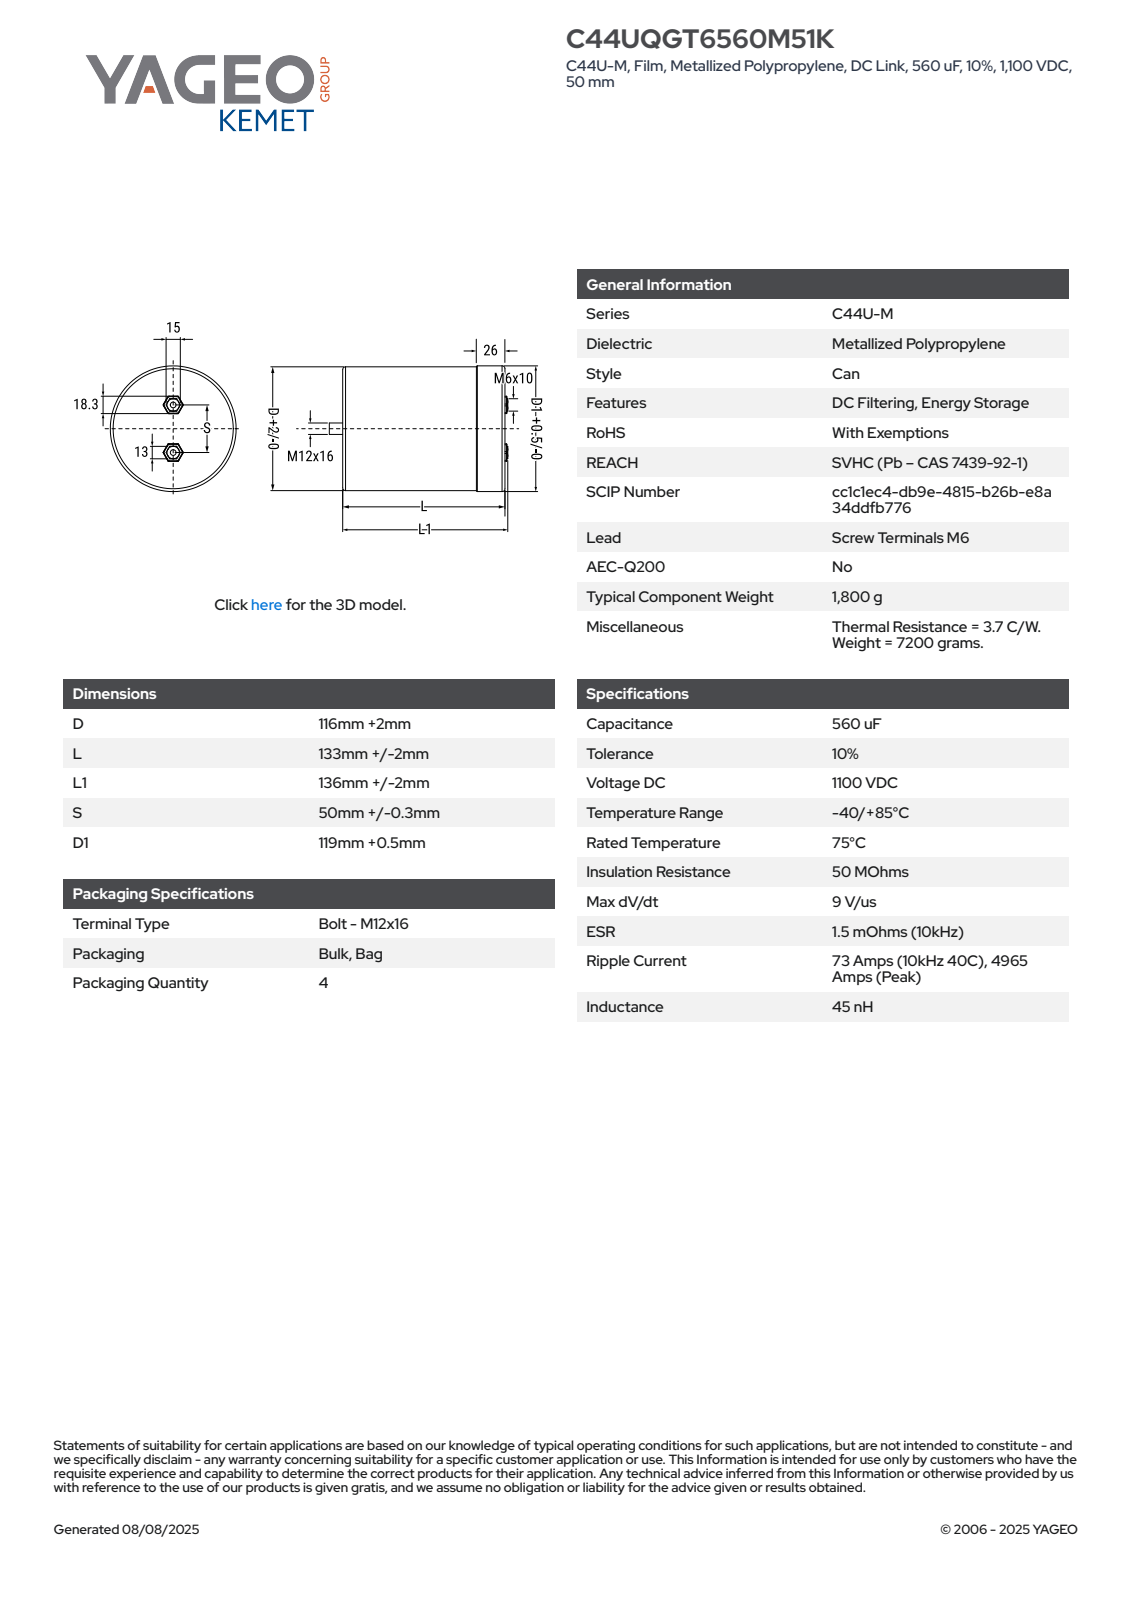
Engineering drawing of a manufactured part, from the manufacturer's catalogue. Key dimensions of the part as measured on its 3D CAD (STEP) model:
Part name (STEP PRODUCT): CFP_C44UMH_116X133_D118L135S50L1138D1119.5
STEP written by: SolidWorks 2014 (AUTOMOTIVE_DESIGN)
Units: millimetres
Bodies: 1 solid, 92 faces (44 planar, 17 cylindrical, 31 other)
Overall size (bounding box): 154 × 119.5 × 119.5
Volume: 1 486 000 mm³ · Surface area: 73 921 mm²
Round holes (diameter × count): ⌀6 ×2
Round bosses / shafts (diameter × count): ⌀13 ×2, ⌀119.5 ×1, ⌀118 ×1, ⌀12 ×1
Partial cylindrical surfaces — rounded edges, fillets, slot ends (radius × count): R59.01 ×1
Main face-to-face distances: 135, 137, 2, 109, 26, 28, 138, 29, 3, 1
Hole centre spacings: 50
